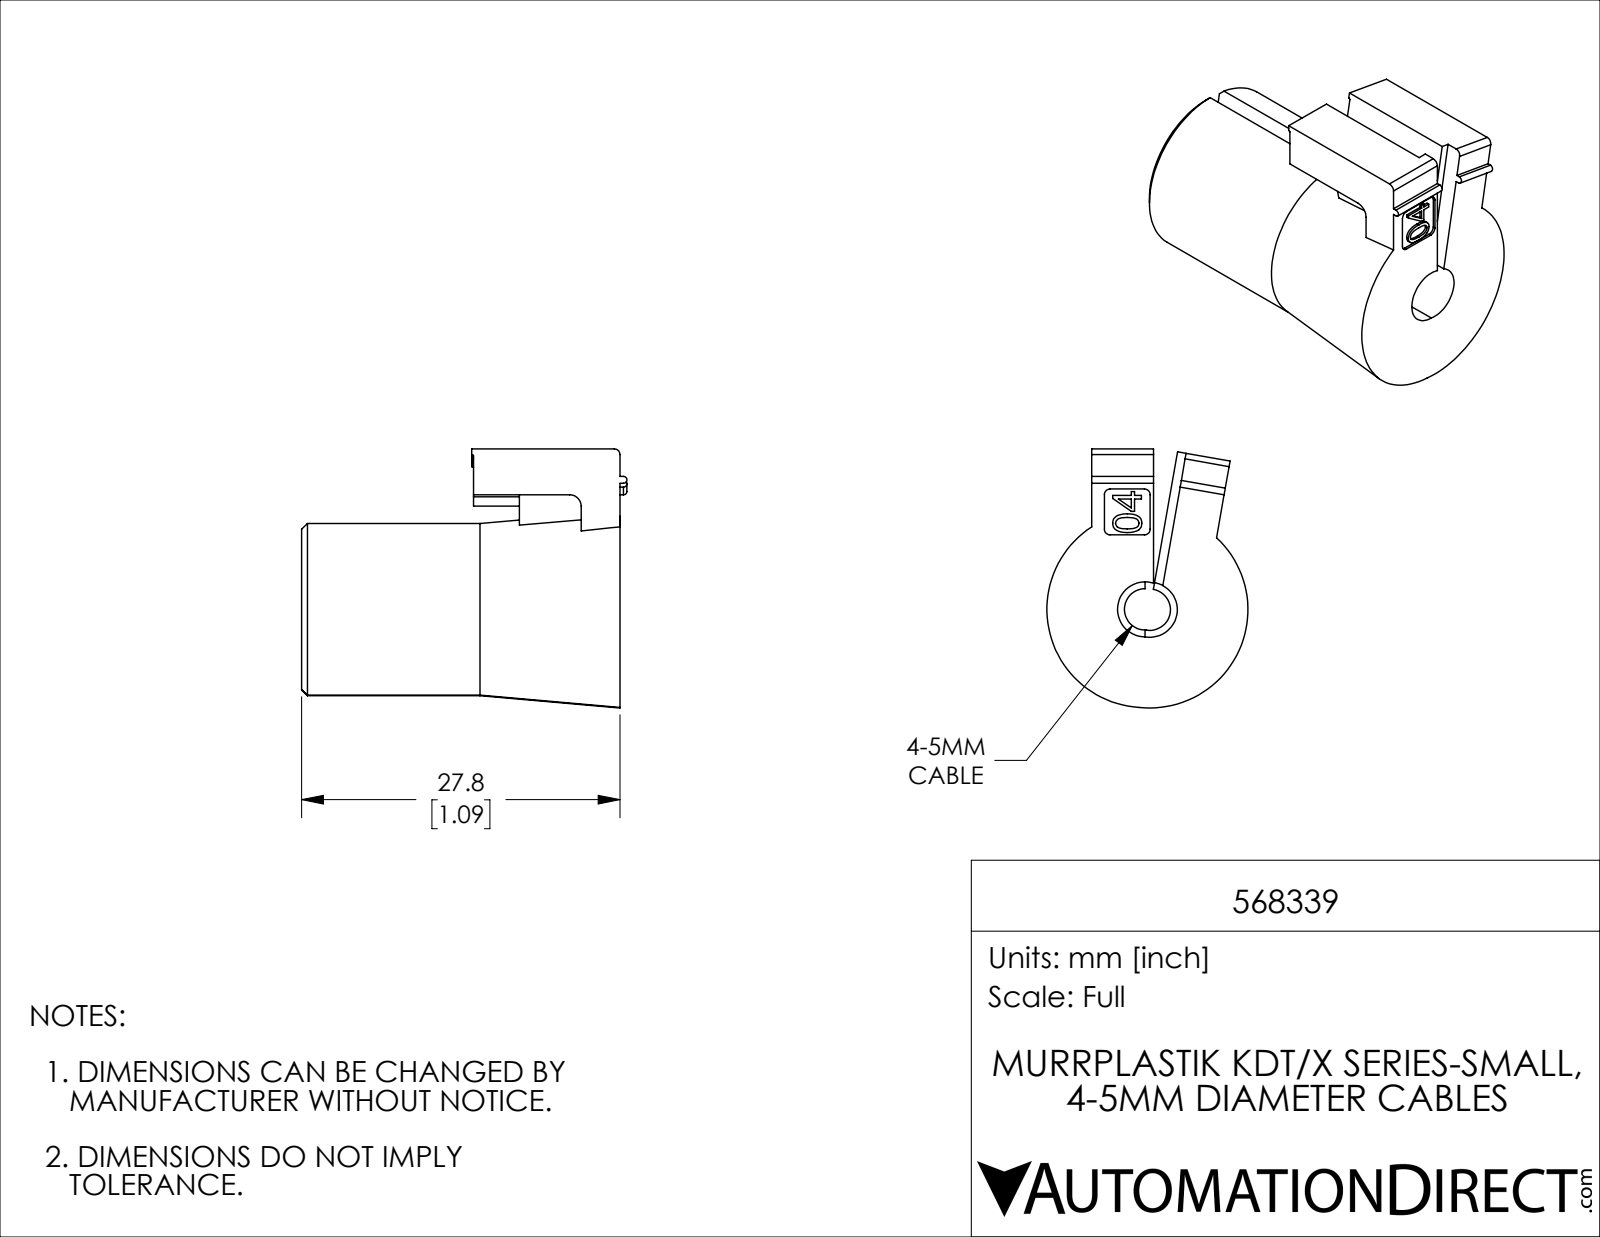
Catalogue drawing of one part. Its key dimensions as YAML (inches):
part_name: "568339"
step_written_by: "SolidWorks 2019 (CONFIG_CONTROL_DESIGN)"
units: inches
bodies: {solids: 1, faces: 109, planar: 62, cylindrical: 24, other: 23}
overall_size: [1.118, 0.89, 0.691]
volume: 0.322
surface_area: 4.568
partial_cylinders:
  - {radius: 0.02, count: 6}
  - {radius: 0.004, count: 2}
  - {radius: 0.012, count: 2}
  - {radius: 0.039, count: 2}
  - {radius: 0.071, count: 2}
  - {radius: 0.094, count: 2}
  - {radius: 0.295, count: 2}
face_to_face_distances: [1.094, 0.157, 0.183, 0.183, 0.504, 0.591, 0.213, 0.154, 0.029, 0.03]
